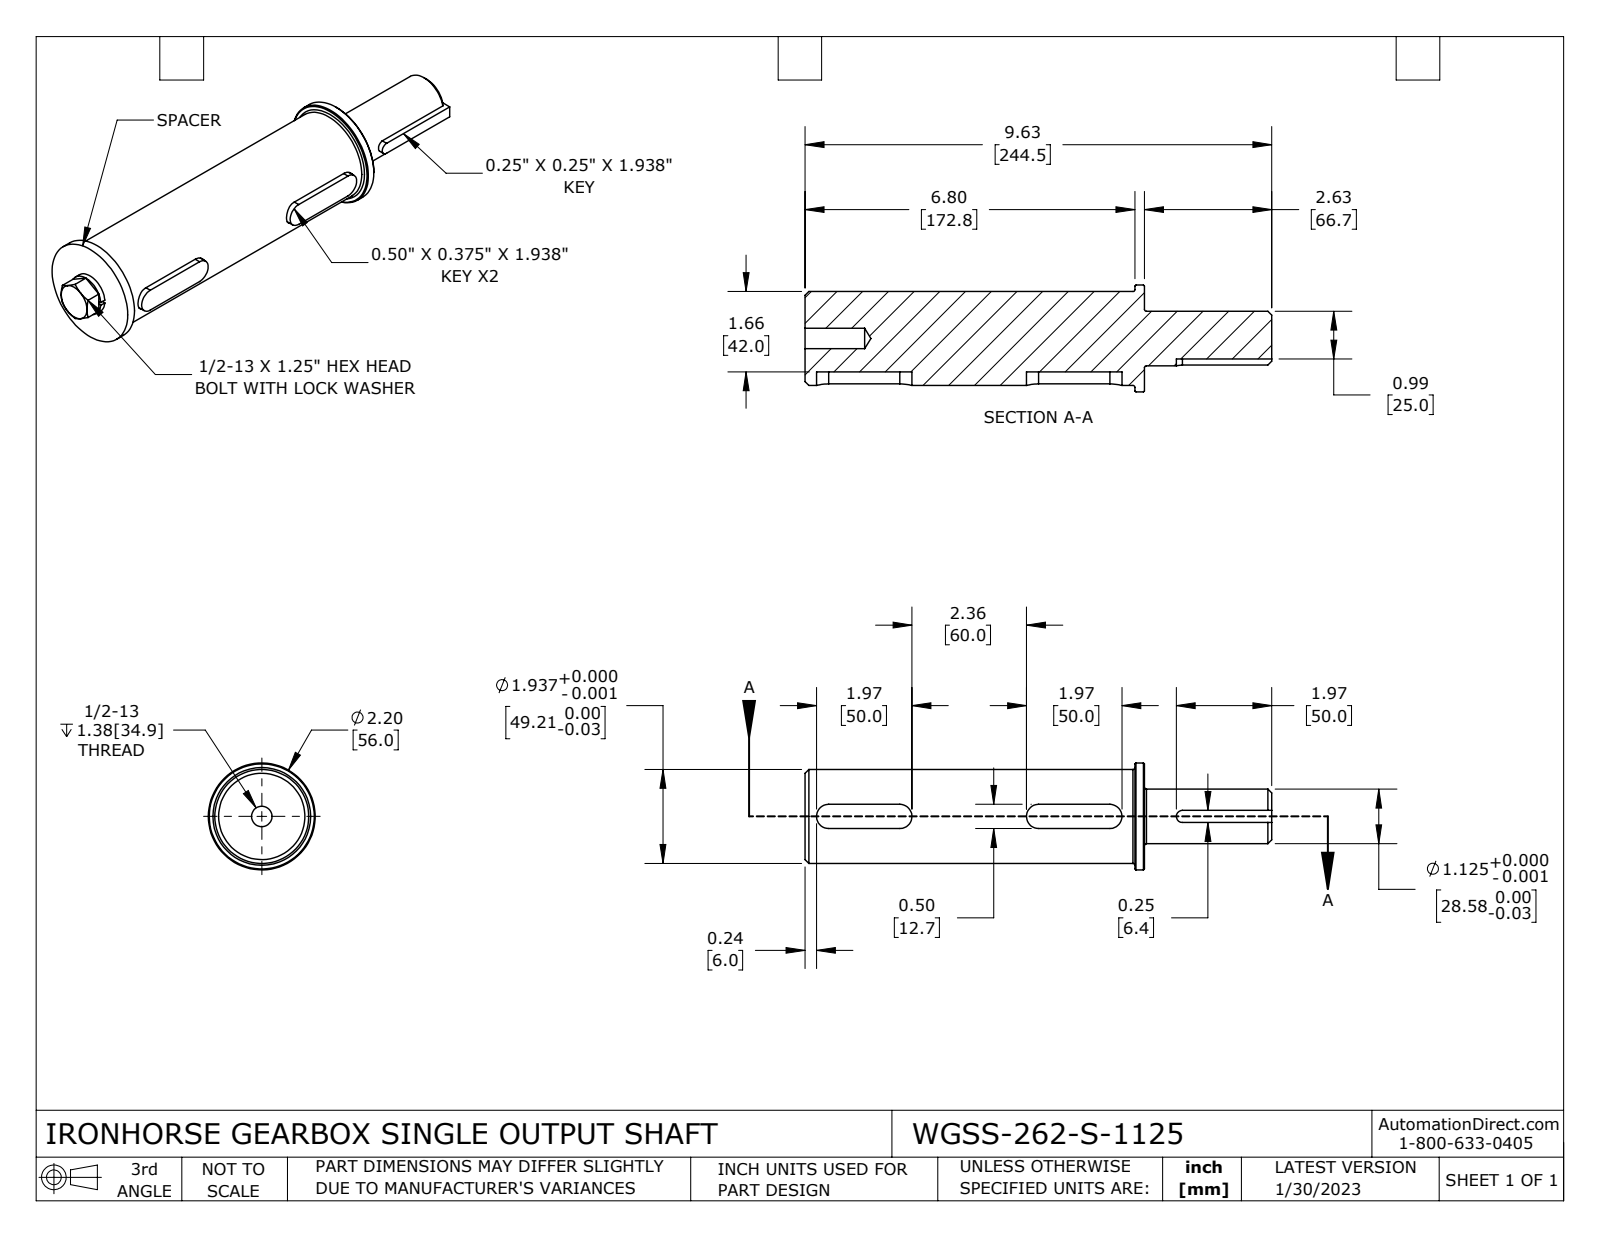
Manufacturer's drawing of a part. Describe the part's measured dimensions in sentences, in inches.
The part is named "WGSS-262-S-1125". Its 3-D file was written by "SolidWorks 2021 (CONFIG_CONTROL_DESIGN)". It is 7 solids with 93 faces: 41 planar, 31 cylindrical and 21 other. Overall it measures 10.285 by 2.205 by 2.205 inches. Its volume is 24.6 cubic inches and its surface area 86.24 square inches. Round holes: 1 of diameter 0.422, 1 of diameter 0.512, 1 of diameter 0.571. Round bosses or shafts: 1 of diameter 2.205, 1 of diameter 1.937, 1 of diameter 1.125, 1 of diameter 0.869, 1 of diameter 0.5. Partial cylindrical surfaces (rounded edges, fillets, slot ends): 8 of radius 0.25, 1 of radius 0.125. The main face-to-face distances are 0.197, 7, 7.197, 0.375, 0.5, 0.263, 0.638, 0.25, 0.125, 0.375.
